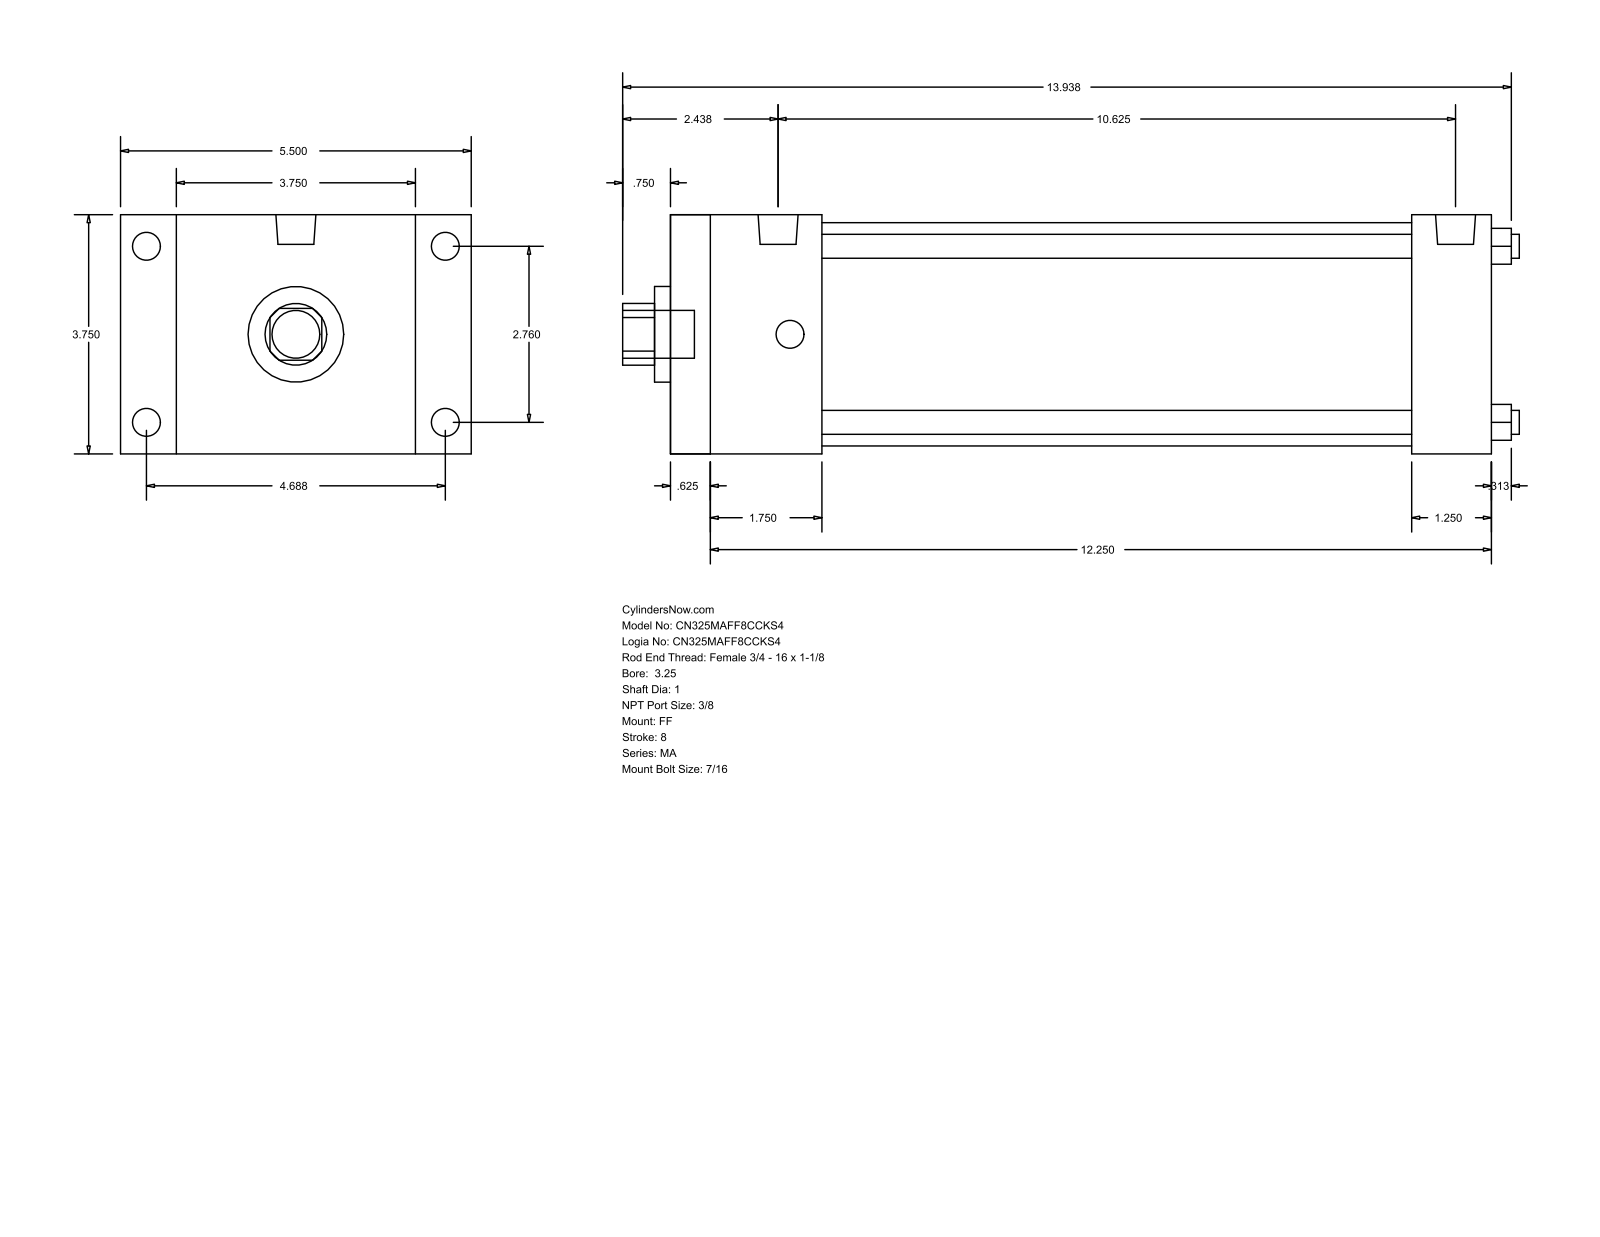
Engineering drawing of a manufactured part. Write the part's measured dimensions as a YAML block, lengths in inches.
part_name: "MA_FF__0325_1"
step_written_by: "GSSL Pune (CONFIG_CONTROL_DESIGN)"
units: inches
bodies: {solids: 0, faces: 92, planar: 64, cylindrical: 28, other: 0}
overall_size: [14.063, 5.5, 3.75]
round_holes:
  - {diameter: 0.375, count: 4}
  - {diameter: 1, count: 1}
  - {diameter: 1.5, count: 1}
  - {diameter: 3.5, count: 1}
round_bosses_or_shafts:
  - {diameter: 0.437, count: 8}
  - {diameter: 0.627, count: 2}
  - {diameter: 0.75, count: 1}
partial_cylinders:
  - {radius: 0.484, count: 1}
face_to_face_distances: [3.75, 12.875, 0.625, 12.25, 0.875, 4.625, 2.375, 11.625, 1.75, 11]
hole_center_spacings: [1.952, 2.76, 3.903]
